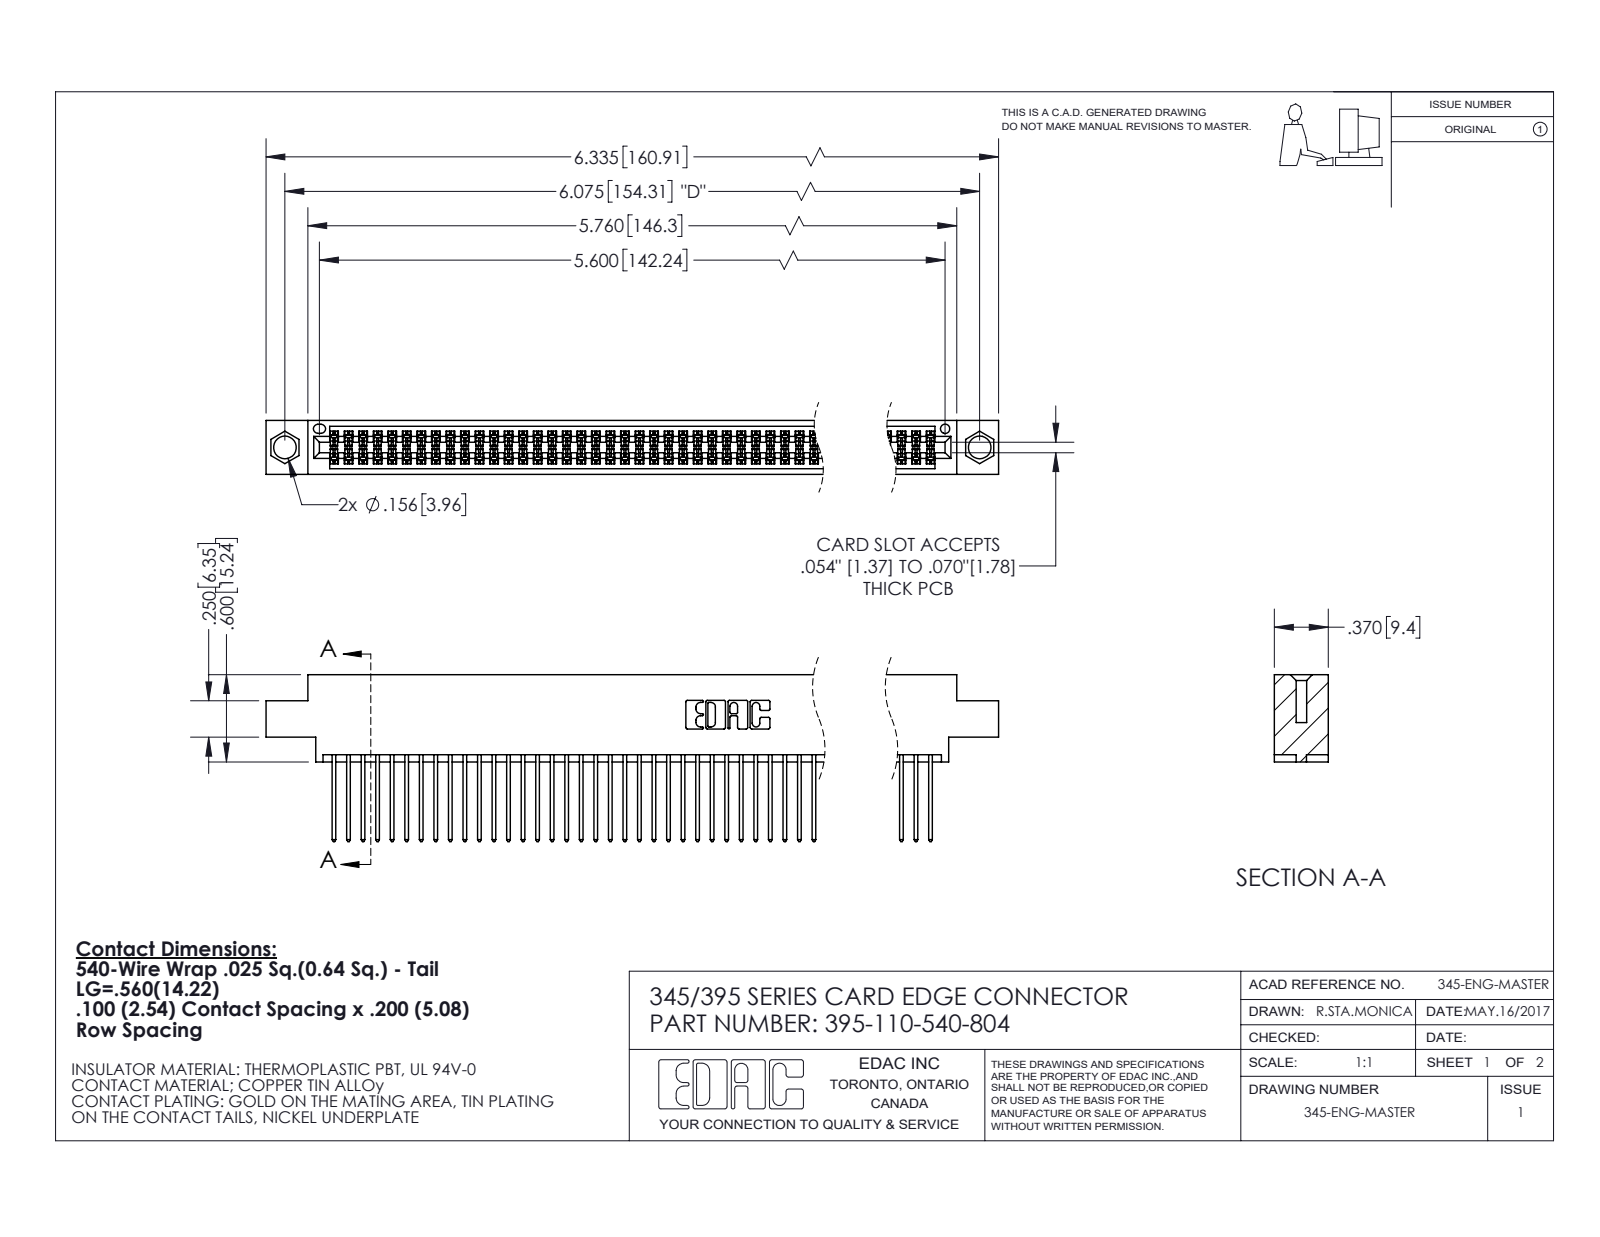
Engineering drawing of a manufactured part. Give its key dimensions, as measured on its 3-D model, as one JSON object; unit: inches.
{"part_name": "345 Part_0.170 Offset - 0.156 Dia-TI; 345-292-001_345-293-140; 395-110-540-804", "step_written_by": "SolidWorks 2020 (CONFIG_CONTROL_DESIGN)", "units": "inches", "bodies": {"solids": 111, "faces": 5644, "planar": 3728, "cylindrical": 1916, "other": 0}, "overall_size": [6.335, 1.147, 0.37], "volume_in3": 0.973, "surface_area_in2": 39.92, "round_holes": [[0.156, 2], [0.064, 1]], "partial_cylinders_radius": [[0.006, 220], [0.01, 110], [0.01, 22], [0.007, 6], [0.031, 6], [0.026, 3], [0.014, 2], [0.019, 2]], "face_to_face_distances": [0.072, 0.298, 0.2, 0.098, 0.272, 0.025, 0.37, 0.225, 0.175, 0.149], "hole_center_spacings": [0.27, 5.839, 6.075]}
